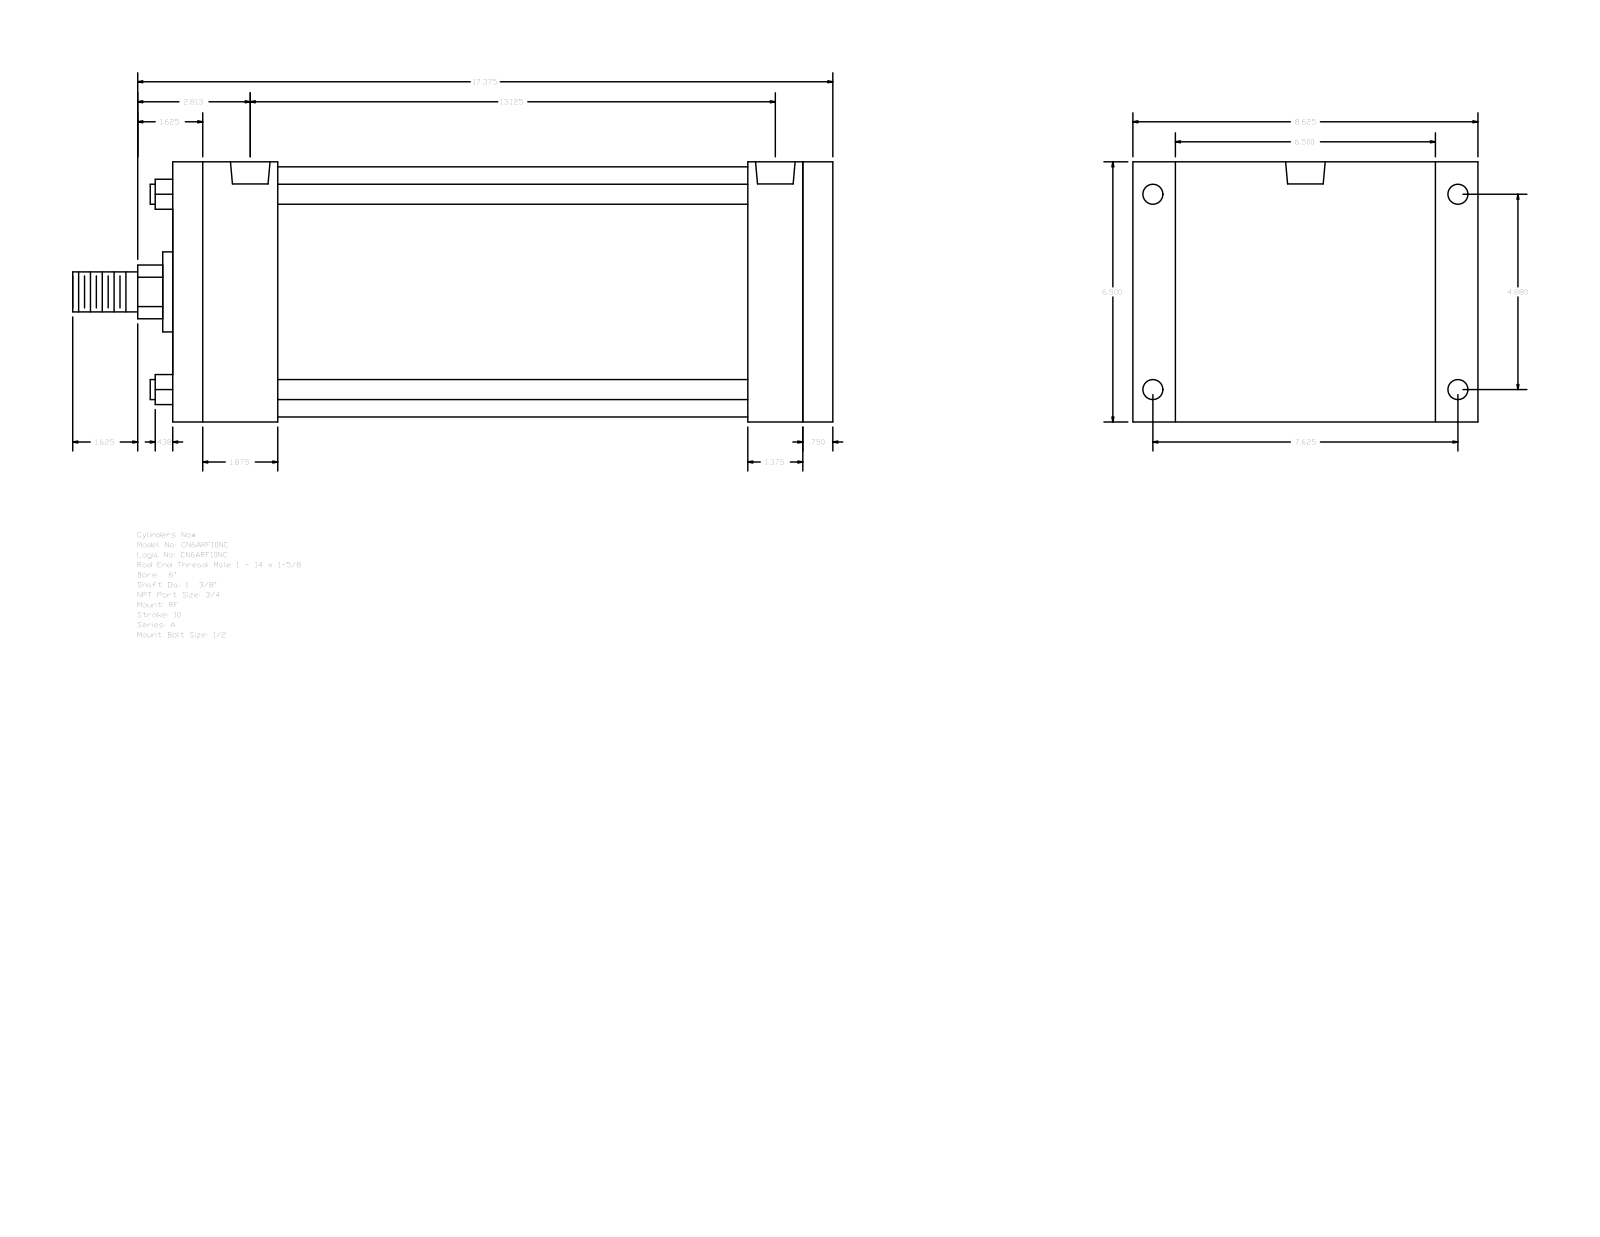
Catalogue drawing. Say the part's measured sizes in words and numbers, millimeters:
The part is named "A_RF__0600_1.375". Its 3-D file was written by "GSSL Pune (CONFIG_CONTROL_DESIGN)". It is 0 solids with 92 faces: 64 planar, 28 cylindrical and 0 other. Overall it measures 482.6 by 219.07 by 165.1 millimeters. Round holes: 4 of diameter 12.7, 4 of diameter 15.08, 2 of diameter 25.12. Round bosses or shafts: 4 of diameter 12.7, 1 of diameter 158.75, 1 of diameter 50.8, 1 of diameter 34.92, 1 of diameter 25.4. Partial cylindrical surfaces (rounded edges, fillets, slot ends): 1 of radius 17.06. The main face-to-face distances are 165.1, 419.09, 19.05, 400.04, 53.97, 66.67, 333.37, 352.42, 365.12, 298.45. The hole center spacings are 5.56, 123.96, 193.68, 229.95, 322.25, 327.81, 333.37.
